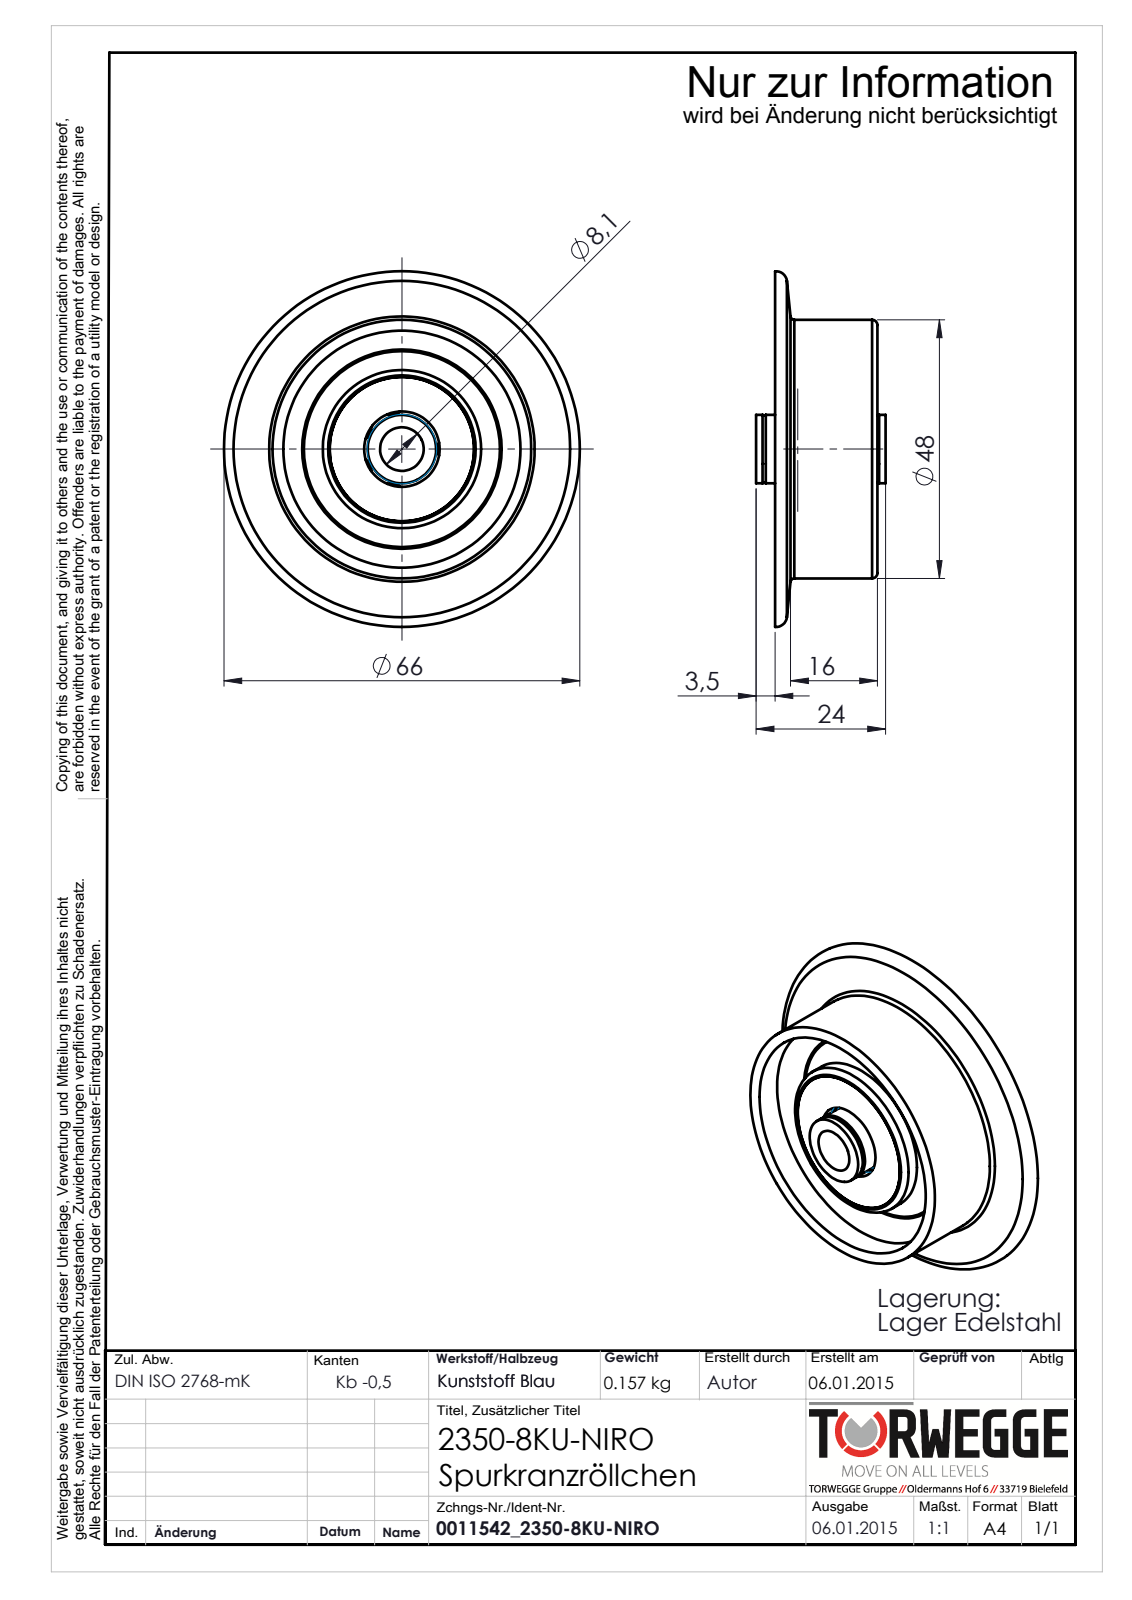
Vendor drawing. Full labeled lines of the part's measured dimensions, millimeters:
Part name (STEP PRODUCT): 0011542_2350-8KU-NIRO
STEP written by: SolidWorks 2014 (AUTOMOTIVE_DESIGN)
Units: millimetres
Bodies: 0 solids, 102 faces (12 planar, 34 cylindrical, 56 other)
Overall size (bounding box): 66.02 × 66.02 × 24
Round holes (diameter × count): ⌀8.1 ×1, ⌀14 ×1, ⌀14.2 ×1, ⌀15.85 ×1, ⌀26.8 ×1, ⌀44 ×1
Round bosses / shafts (diameter × count): ⌀48 ×1, ⌀29.36 ×1, ⌀12.7 ×1
Main face-to-face distances: 3.9, 20.1, 16.2, 24, 10.6, 6.7, 9.5, 13.4, 8.4, 16.3
